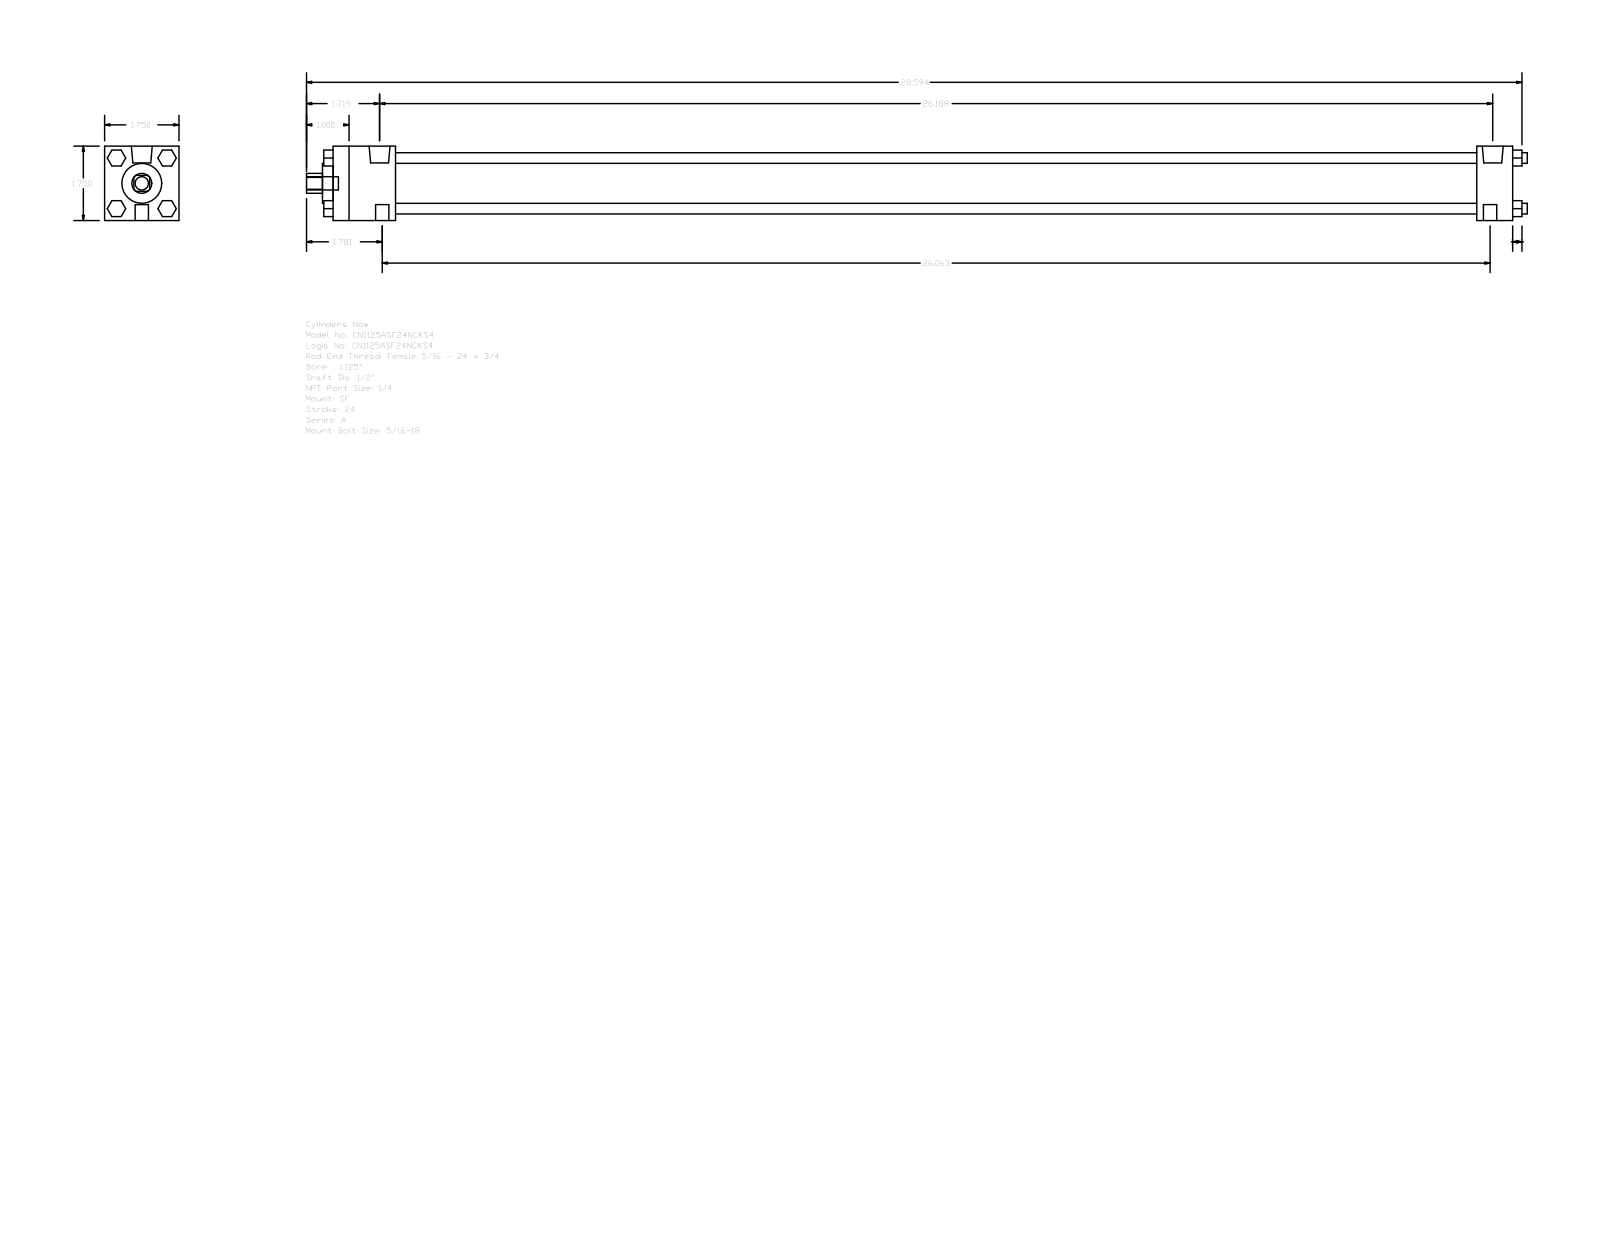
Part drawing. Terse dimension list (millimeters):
name: A_SF__0112_0.5
written by: GSSL Pune (CONFIG_CONTROL_DESIGN)
unit: mm
bodies: 0 solids, 120 faces (92 planar, 28 cylindrical, 0 other)
size: 729.46 × 44.45 × 44.45
holes: 1× ⌀12.7, 1× ⌀23.81, 1× ⌀31.88
bosses: 4× ⌀6.35, 3× ⌀7.94, 2× ⌀12.49, 2× ⌀5.56
rounds: 1× R5.94
face distances: 44.46, 704.85, 683.41, 21.44, 37.3, 646.11, 667.55, 9.53, 5.59, 9.52
